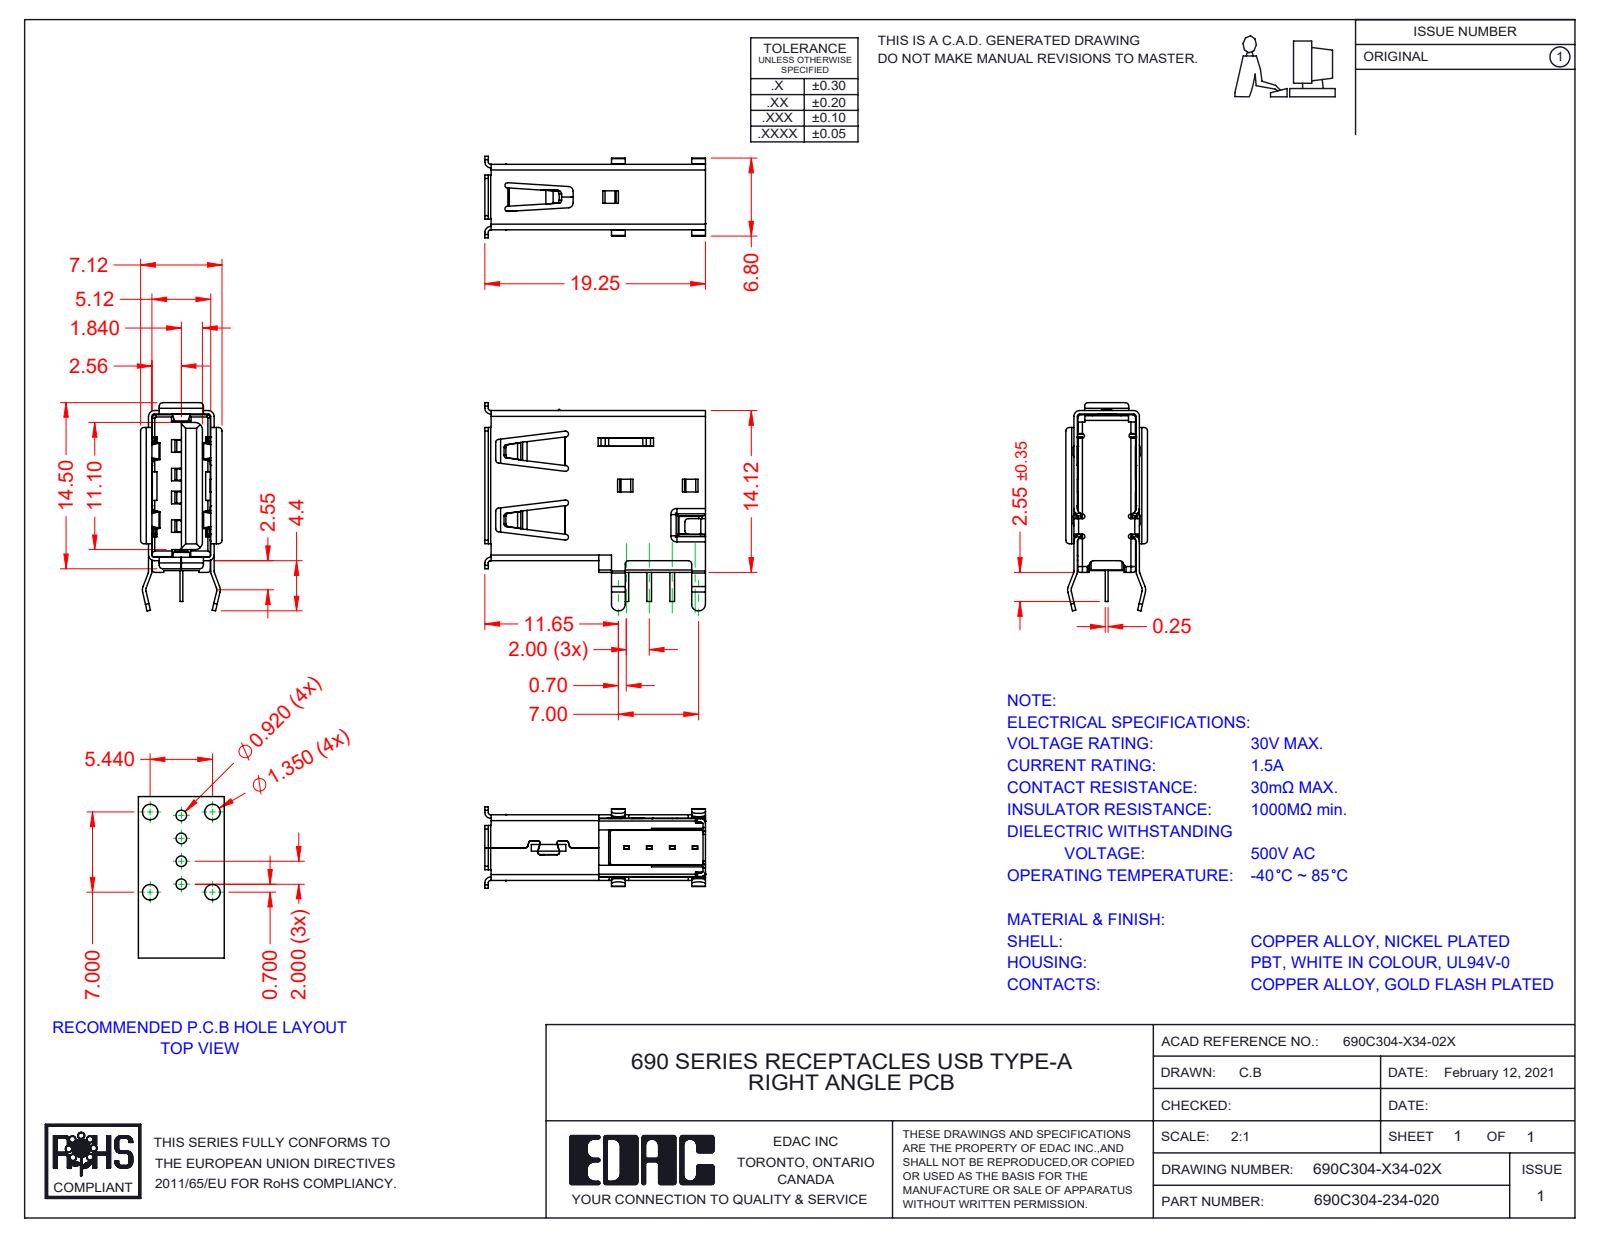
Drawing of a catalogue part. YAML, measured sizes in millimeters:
part_name: "Contact1 690C304-X34-02X; Shell 690C304-X34-02X; Contact2 690C304-X34-02X; Insulator 690C304-X34-02X (+3 more)"
step_written_by: "SolidWorks 2020 (AUTOMOTIVE_DESIGN)"
units: millimeters
bodies: {solids: 6, faces: 1391, planar: 890, cylindrical: 426, other: 75}
overall_size: [19.25, 18.2, 7.12]
volume: 664
surface_area: 2808
partial_cylinders:
  - {radius: 0.3, count: 59}
  - {radius: 0.15, count: 38}
  - {radius: 0.2, count: 35}
  - {radius: 0.13, count: 24}
  - {radius: 0.4, count: 23}
  - {radius: 0.6, count: 22}
  - {radius: 0.25, count: 20}
  - {radius: 0.1, count: 15}
face_to_face_distances: [5.42, 5.12, 5.72, 2.86, 2.56, 1.02, 12.8, 4.4, 1.27, 1.1]
